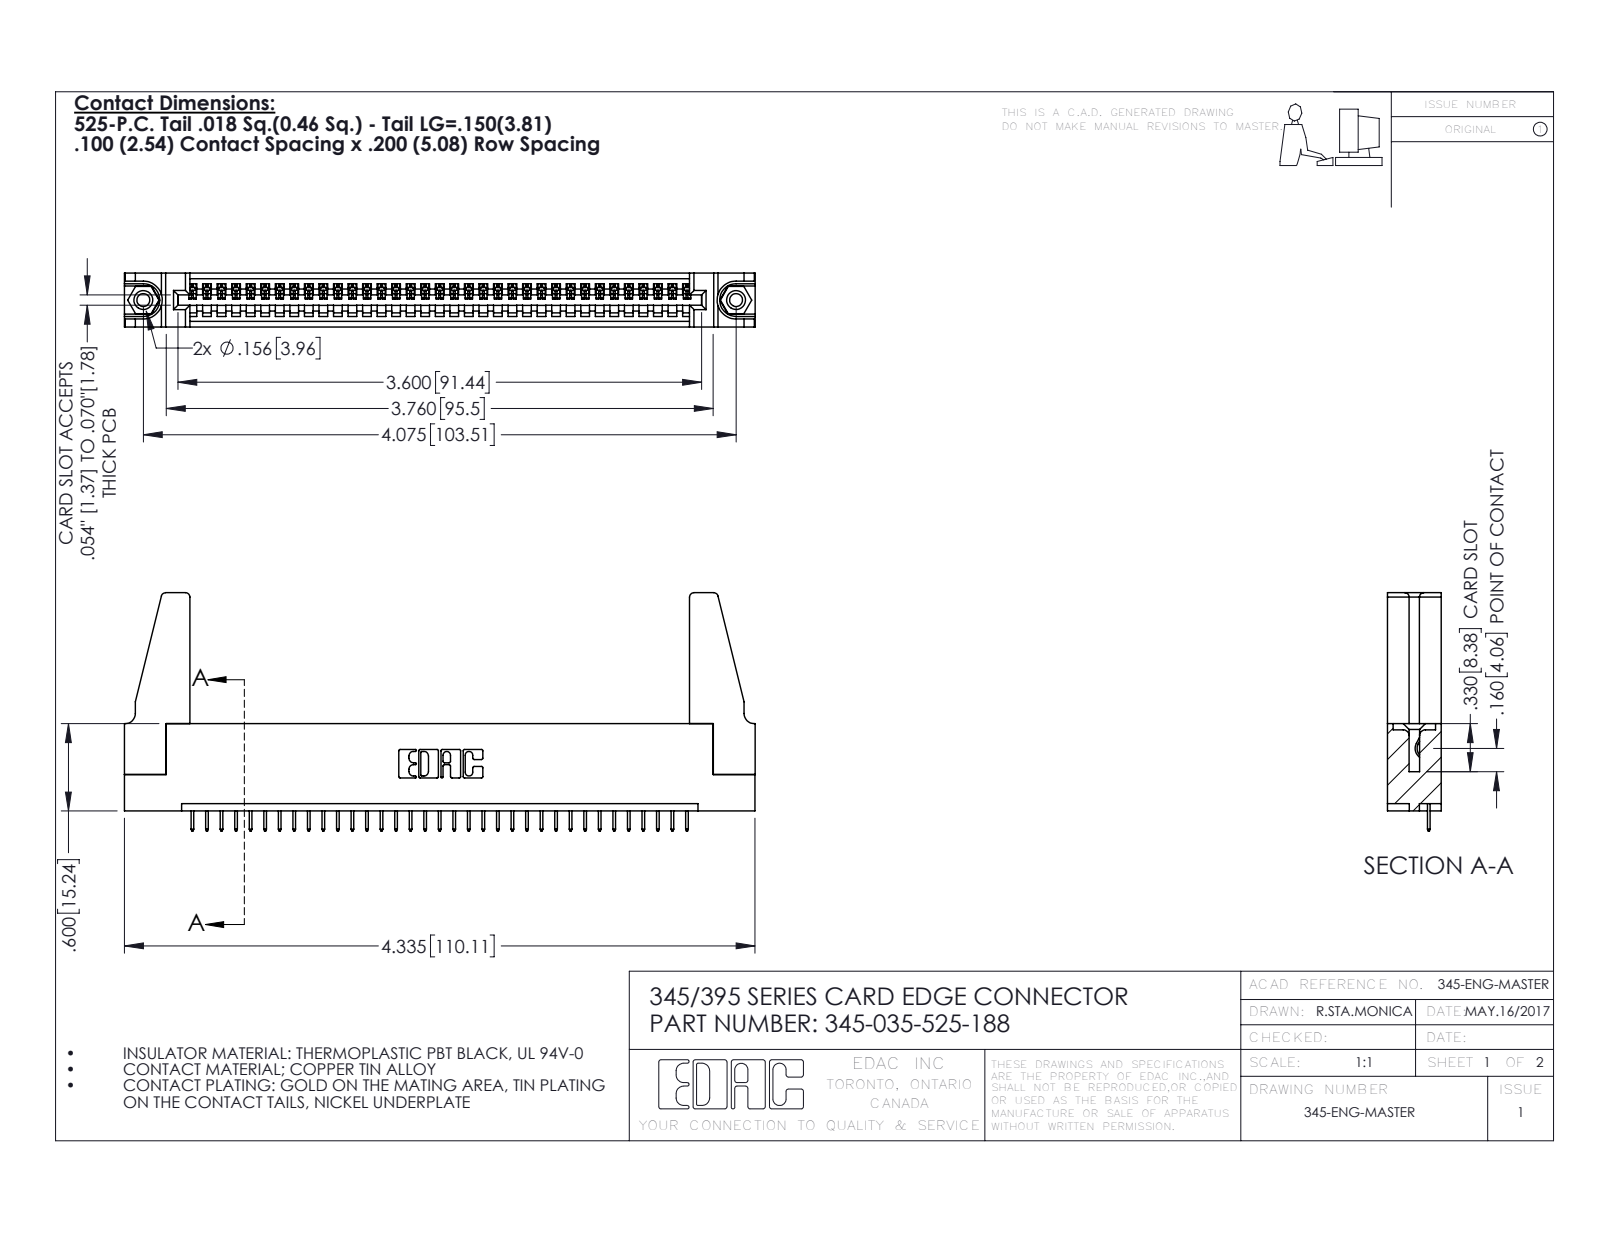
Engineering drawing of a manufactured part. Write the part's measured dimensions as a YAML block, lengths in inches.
part_name: "345-220-078_345-220-088; 345-292-001_345-293-125; 345-250-001_345-250-001-102; 345-035-525-188 (+1 more)"
step_written_by: "SolidWorks 2020 (CONFIG_CONTROL_DESIGN)"
units: inches
bodies: {solids: 40, faces: 2420, planar: 1762, cylindrical: 642, other: 16}
overall_size: [4.336, 1.637, 0.37]
volume: 0.825
surface_area: 25.1
round_holes:
  - {diameter: 0.089, count: 2}
  - {diameter: 0.125, count: 2}
  - {diameter: 0.156, count: 2}
  - {diameter: 0.064, count: 1}
round_bosses_or_shafts:
  - {diameter: 0.155, count: 2}
partial_cylinders:
  - {radius: 0.006, count: 70}
  - {radius: 0.01, count: 22}
  - {radius: 0.03, count: 8}
  - {radius: 0.007, count: 6}
  - {radius: 0.031, count: 6}
  - {radius: 0.026, count: 3}
  - {radius: 0.031, count: 2}
  - {radius: 0.04, count: 2}
face_to_face_distances: [0.072, 0.37, 0.298, 0.2, 0.098, 0.272, 0.025, 0.225, 0.072, 0.149]
hole_center_spacings: [0.27, 3.839, 4.075]
